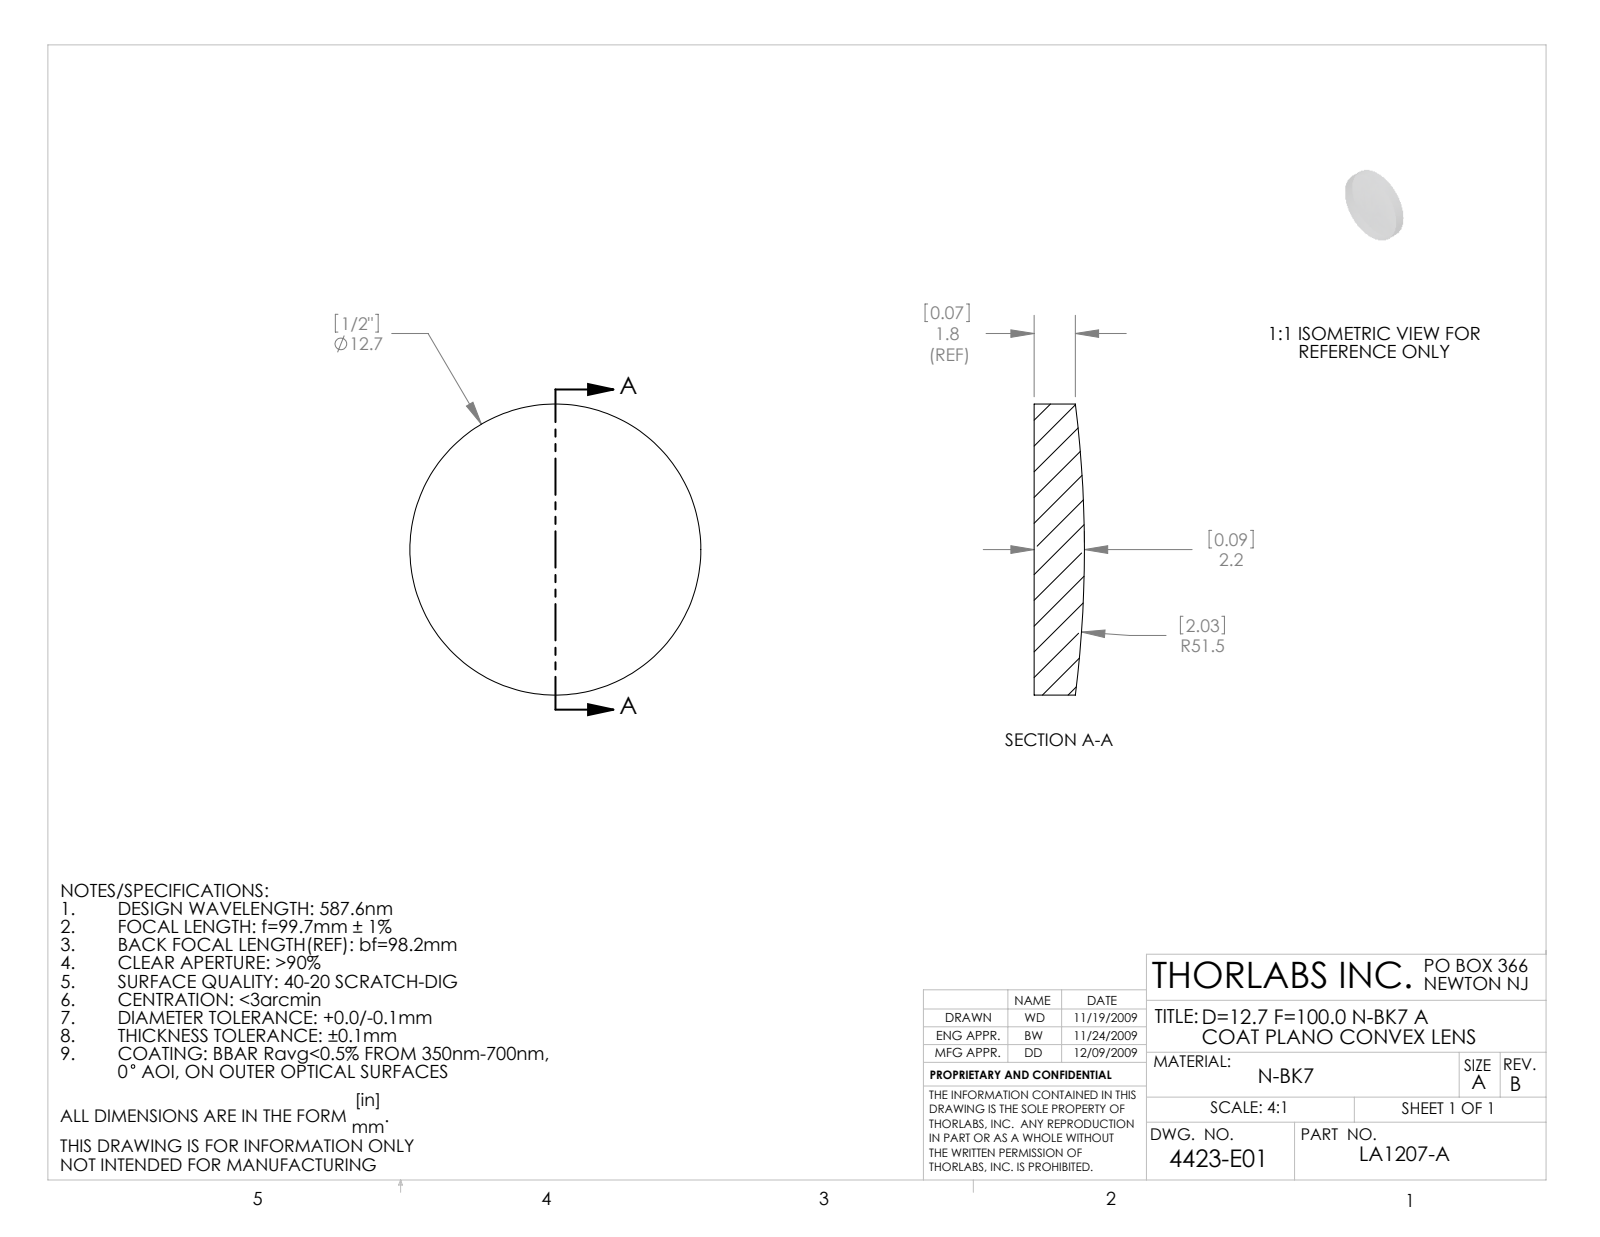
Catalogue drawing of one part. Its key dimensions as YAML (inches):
part_name: "4423-E0W"
step_written_by: "SolidWorks 2009 (AUTOMOTIVE_DESIGN)"
units: inches
bodies: {solids: 1, faces: 5, planar: 1, cylindrical: 2, other: 2}
overall_size: [0.5, 0.5, 0.086]
volume: 0.015
surface_area: 0.505
round_bosses_or_shafts:
  - {diameter: 0.5, count: 1}
